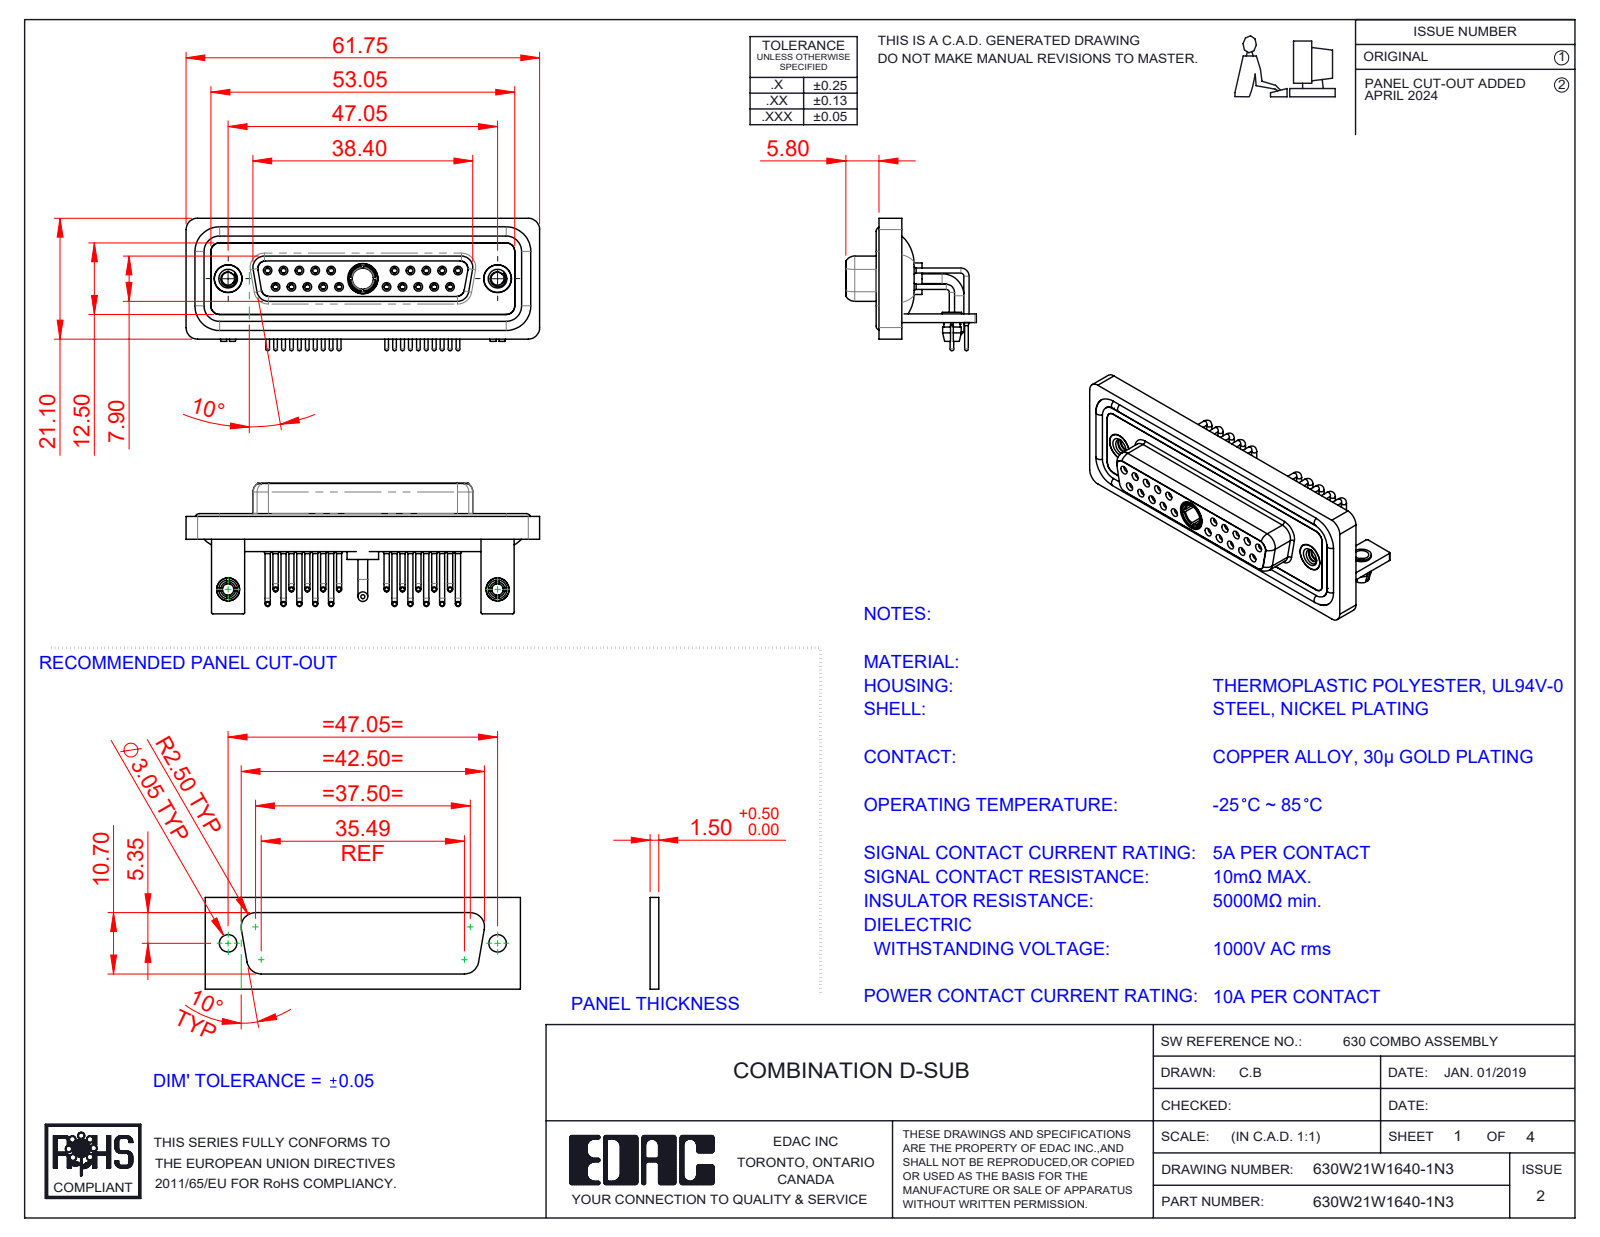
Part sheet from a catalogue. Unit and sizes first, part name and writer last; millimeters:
Units: millimetres
Overall size (bounding box): 61.75 × 23.12 × 22.8
Round holes (diameter × count): ⌀2 ×22, ⌀0.9 ×20, ⌀1.1 ×20, ⌀1.5 ×20, ⌀1.6 ×10, ⌀1.7 ×10, ⌀4.85 ×3, ⌀2.26 ×2, ⌀2.5 ×2, ⌀3.2 ×2, ⌀4 ×2, ⌀4.05 ×2
Round bosses / shafts (diameter × count): ⌀0.9 ×20, ⌀0.65 ×20, ⌀1.6 ×14, ⌀4.95 ×2, ⌀4.8 ×2, ⌀4 ×2, ⌀3.4 ×2, ⌀3.3 ×2
Partial cylindrical surfaces — rounded edges, fillets, slot ends (radius × count): R2 ×19, R1.5 ×18, R0.25 ×16, R1.35 ×8, R1.6 ×8, R0.5 ×5, R0.6 ×4, R0.65 ×4
Main face-to-face distances: 0.4, 1.8, 2.9, 3.7, 1.5, 4.1, 1.1, 1.4, 1.6, 2.5
Hole centre spacings: 3.16, 2.77, 5.54, 8.31, 5.04, 19.39, 20.97, 22.16
Volume: 8 851 mm³ · Surface area: 15 675 mm²
Bodies: 33 solids, 1664 faces (502 planar, 729 cylindrical, 433 other)
Part name (STEP PRODUCT): 630Combo Waterproof Housing_25 Contacts; Power Socket_10A RA; 630Combo Threaded Rivet_2; 630Combo Board Lock_50 Contacts (+7 more)
STEP written by: SolidWorks 2023 (CONFIG_CONTROL_DESIGN)
